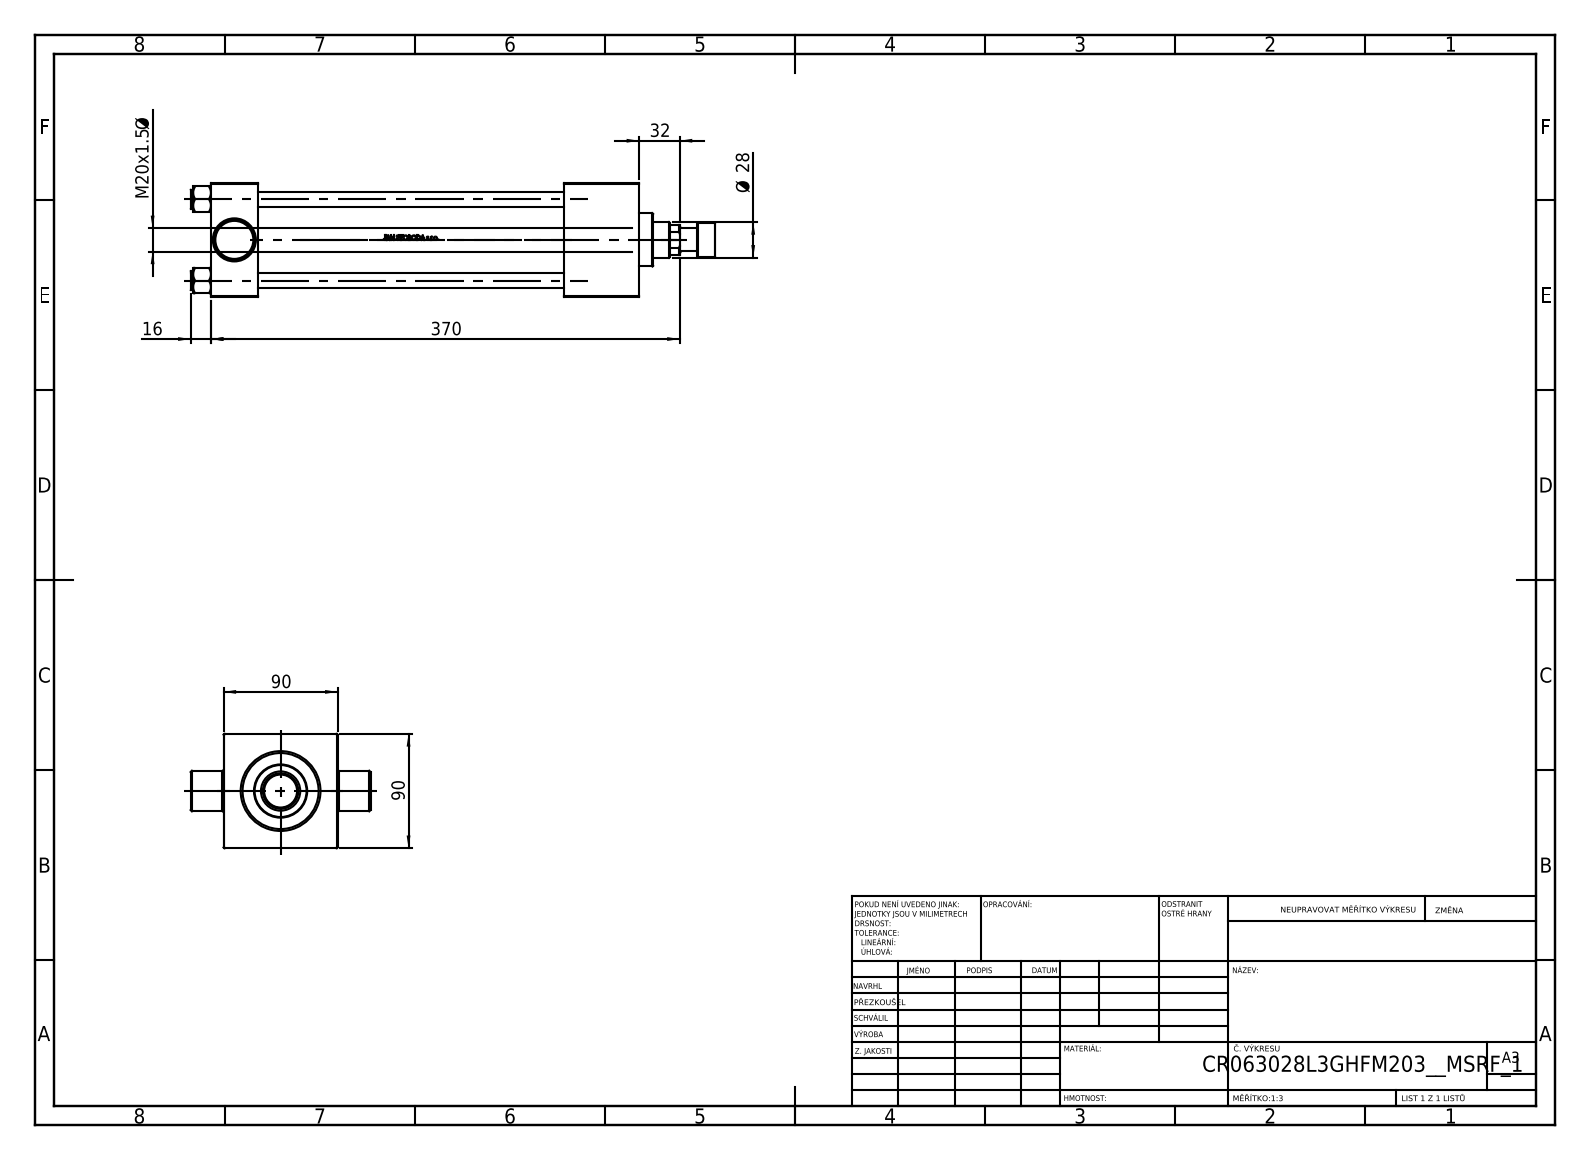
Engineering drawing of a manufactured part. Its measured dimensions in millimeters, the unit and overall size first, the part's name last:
Units: millimetres
Overall size (bounding box): 414 × 142 × 90
Round holes (diameter × count): ⌀12 ×4, ⌀7 ×1, ⌀18.5 ×1, ⌀28 ×1, ⌀31 ×1, ⌀50 ×1, ⌀60 ×1, ⌀63 ×1
Round bosses / shafts (diameter × count): ⌀15 ×4, ⌀69 ×1, ⌀42 ×1, ⌀32 ×1, ⌀27 ×1, ⌀18 ×1
Main face-to-face distances: 90, 37, 338, 301, 89, 59, 0.5, 242, 279, 89.5
Hole centre spacings: 45.47, 64.3, 90.93
Volume: 1 324 000 mm³ · Surface area: 299 557 mm²
Bodies: 12 solids, 1071 faces (429 planar, 114 cylindrical, 528 other)
Part name (STEP PRODUCT): V215CR_L_TYCINKA; V215CR_L_Body; V215CR_VCP_L; V215_VC_A (+2 more)
STEP written by: SolidWorks 2019 (CONFIG_CONTROL_DESIGN)
